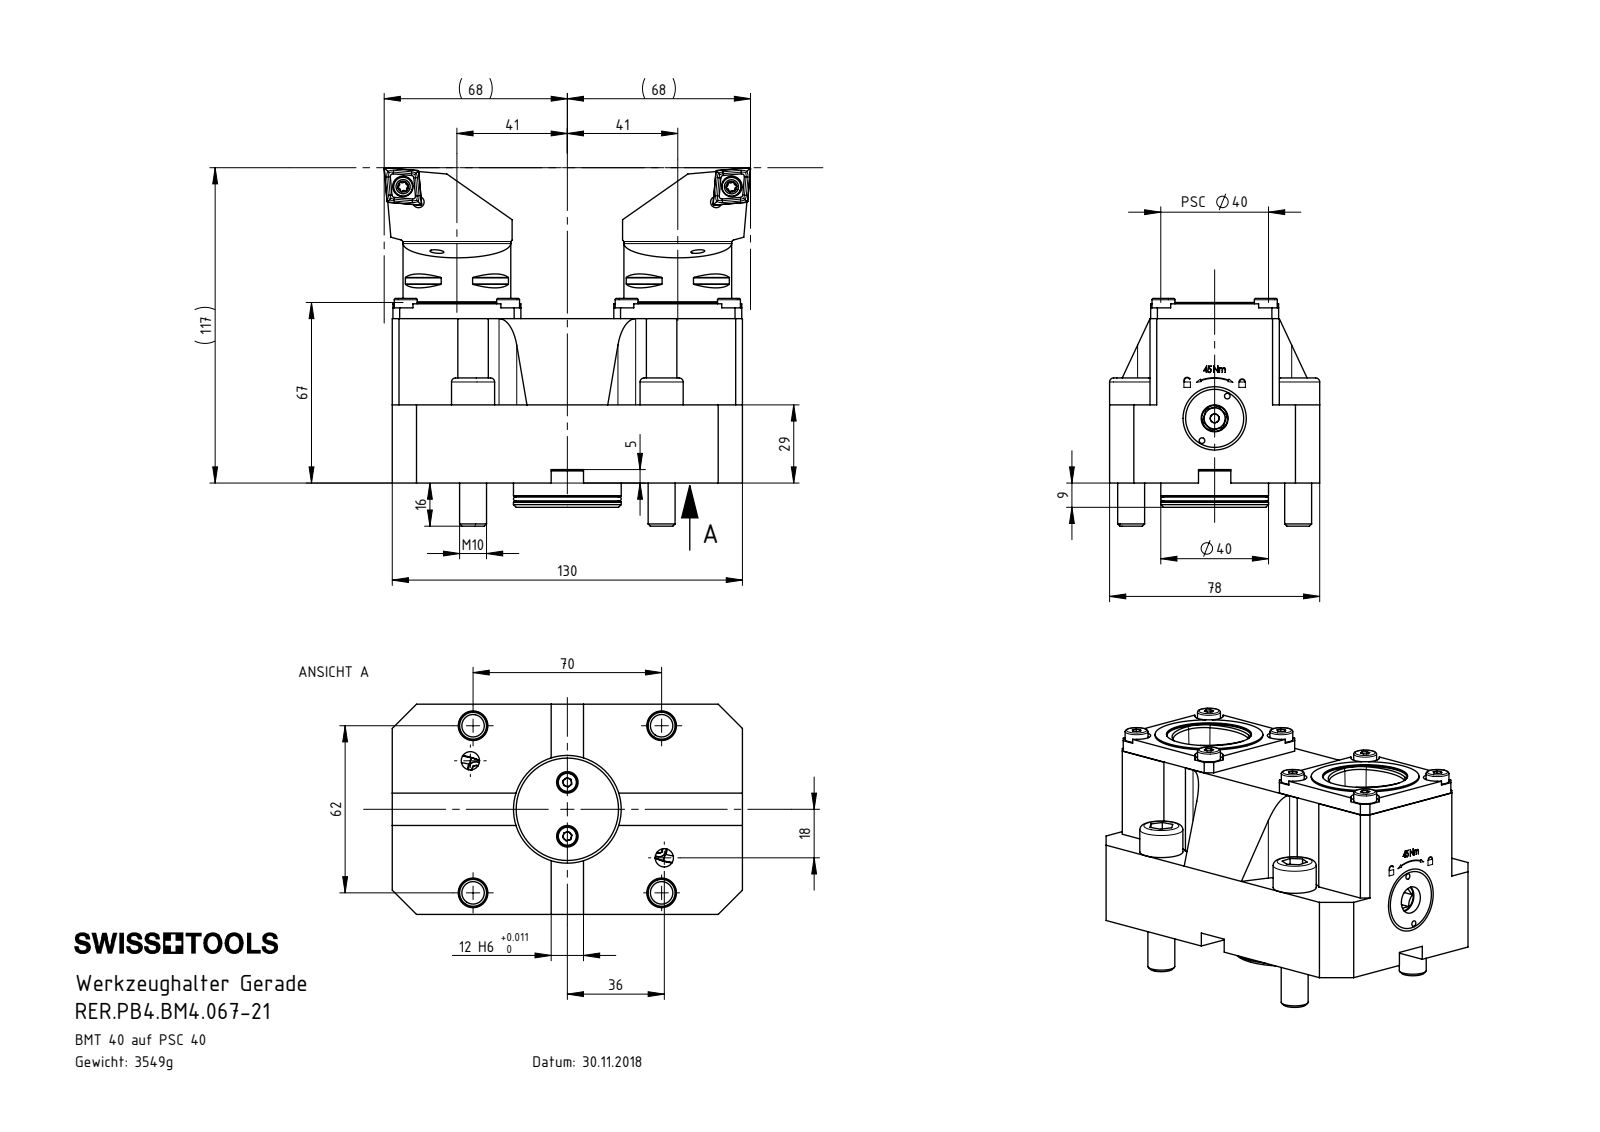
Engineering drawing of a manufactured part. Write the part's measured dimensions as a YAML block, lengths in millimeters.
part_name: "BM4-ER1.040.014; U40-PS4.BER.006; DIN 3771 - 38x1.5; O-Ring_1.50-AD12.00 (+8 more)"
step_written_by: "SolidWorks 2017 (AUTOMOTIVE_DESIGN)"
units: millimeters
bodies: {solids: 65, faces: 1696, planar: 722, cylindrical: 377, other: 597}
overall_size: [130, 84.5, 78]
volume: 499803
surface_area: 149877
round_holes:
  - {diameter: 2.5, count: 10}
  - {diameter: 4.2, count: 10}
  - {diameter: 5.5, count: 8}
  - {diameter: 3.3, count: 7}
  - {diameter: 2.1, count: 4}
  - {diameter: 11, count: 4}
  - {diameter: 4.3, count: 2}
  - {diameter: 6, count: 2}
  - {diameter: 6.5, count: 2}
  - {diameter: 6.8, count: 2}
  - {diameter: 8, count: 2}
  - {diameter: 12, count: 2}
round_bosses_or_shafts:
  - {diameter: 5, count: 10}
  - {diameter: 8.5, count: 8}
  - {diameter: 16, count: 7}
  - {diameter: 10, count: 4}
  - {diameter: 5.5, count: 4}
  - {diameter: 3, count: 4}
  - {diameter: 40, count: 2}
  - {diameter: 39.7, count: 2}
partial_cylinders:
  - {radius: 4, count: 12}
  - {radius: 5.25, count: 8}
  - {radius: 9, count: 5}
  - {radius: 3, count: 4}
  - {radius: 7, count: 4}
  - {radius: 0.2, count: 2}
  - {radius: 4.5, count: 2}
  - {radius: 9.05, count: 2}
face_to_face_distances: [61, 56, 5, 15, 63, 78, 29, 24, 32, 130]
hole_center_spacings: [82, 26.87, 38, 42.2, 17.69, 23.77, 27.73, 29.07]
